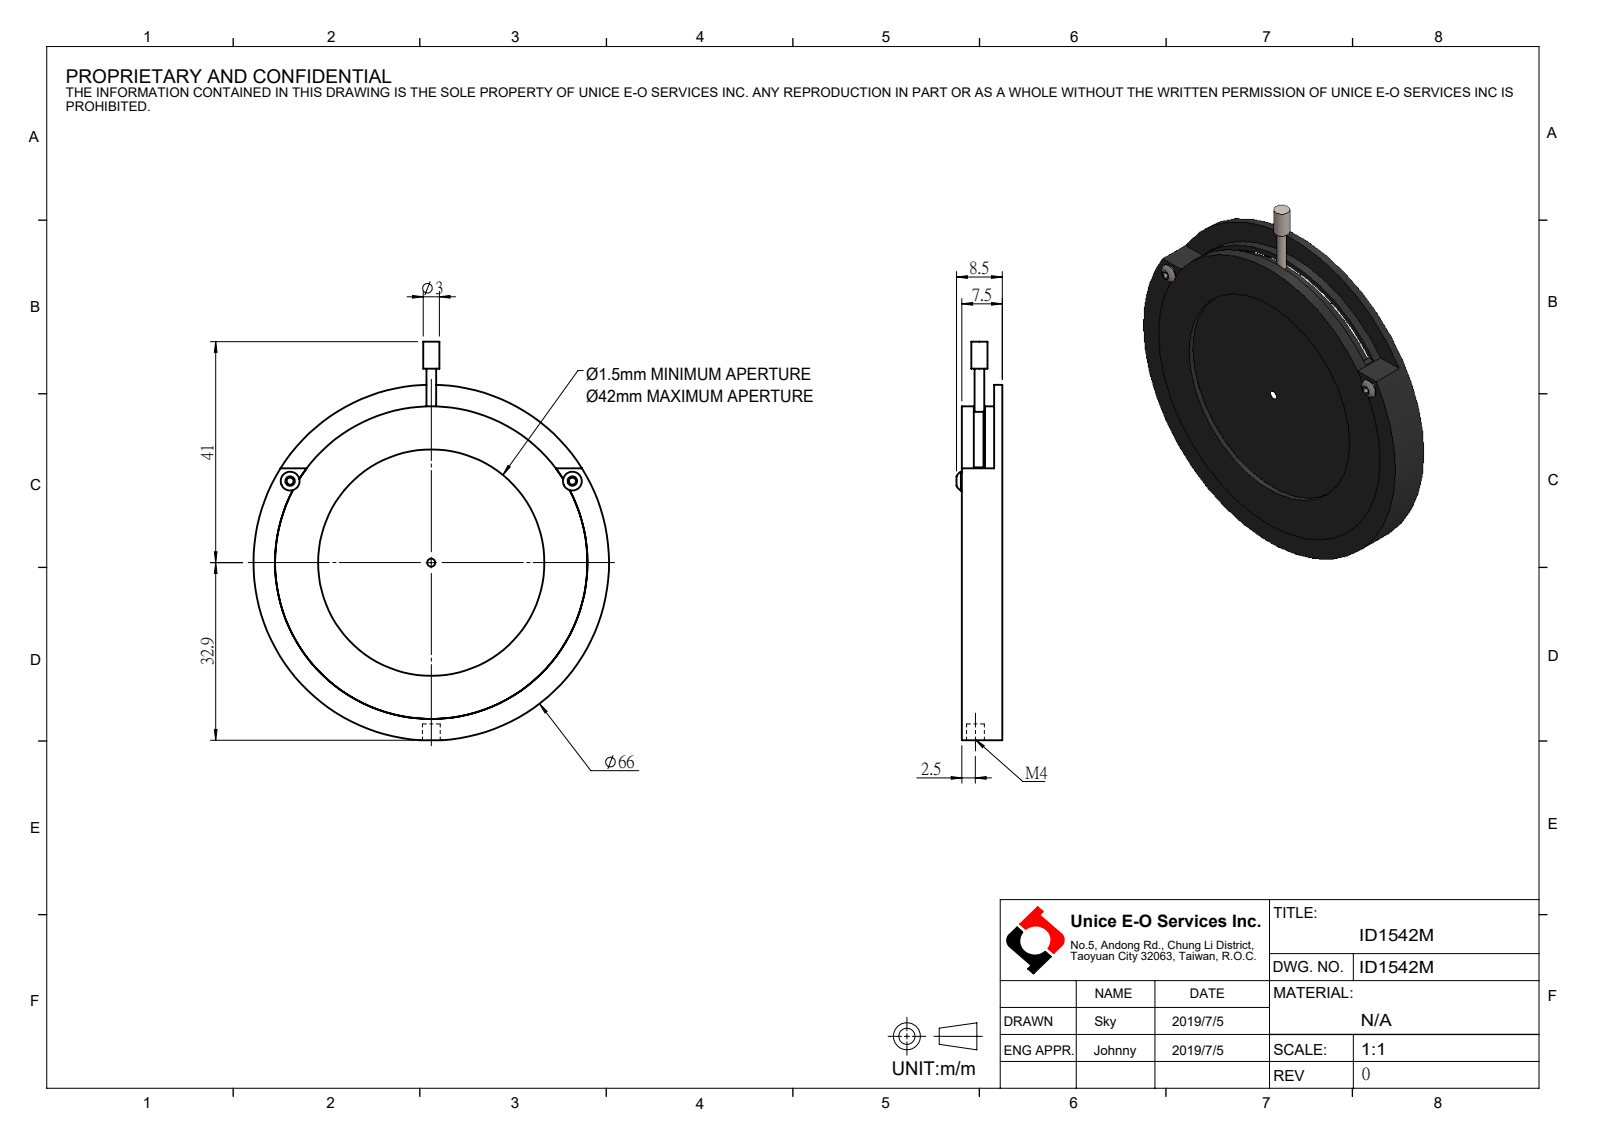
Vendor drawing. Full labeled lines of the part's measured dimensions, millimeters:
Part name (STEP PRODUCT): ID1542M
STEP written by: SolidWorks 2016 (AUTOMOTIVE_DESIGN)
Units: millimetres
Bodies: 0 solids, 63 faces (31 planar, 28 cylindrical, 4 other)
Overall size (bounding box): 73.94 × 66 × 8.5
Round holes (diameter × count): ⌀1.3 ×1, ⌀3.3 ×1, ⌀42 ×1, ⌀55 ×1, ⌀56 ×1, ⌀58 ×1
Round bosses / shafts (diameter × count): ⌀3.5 ×2, ⌀66 ×1, ⌀3 ×1, ⌀1.8 ×1
Main face-to-face distances: 1.1, 1, 2.9, 3, 4, 3.5, 6.4, 6.5, 7.5, 5
